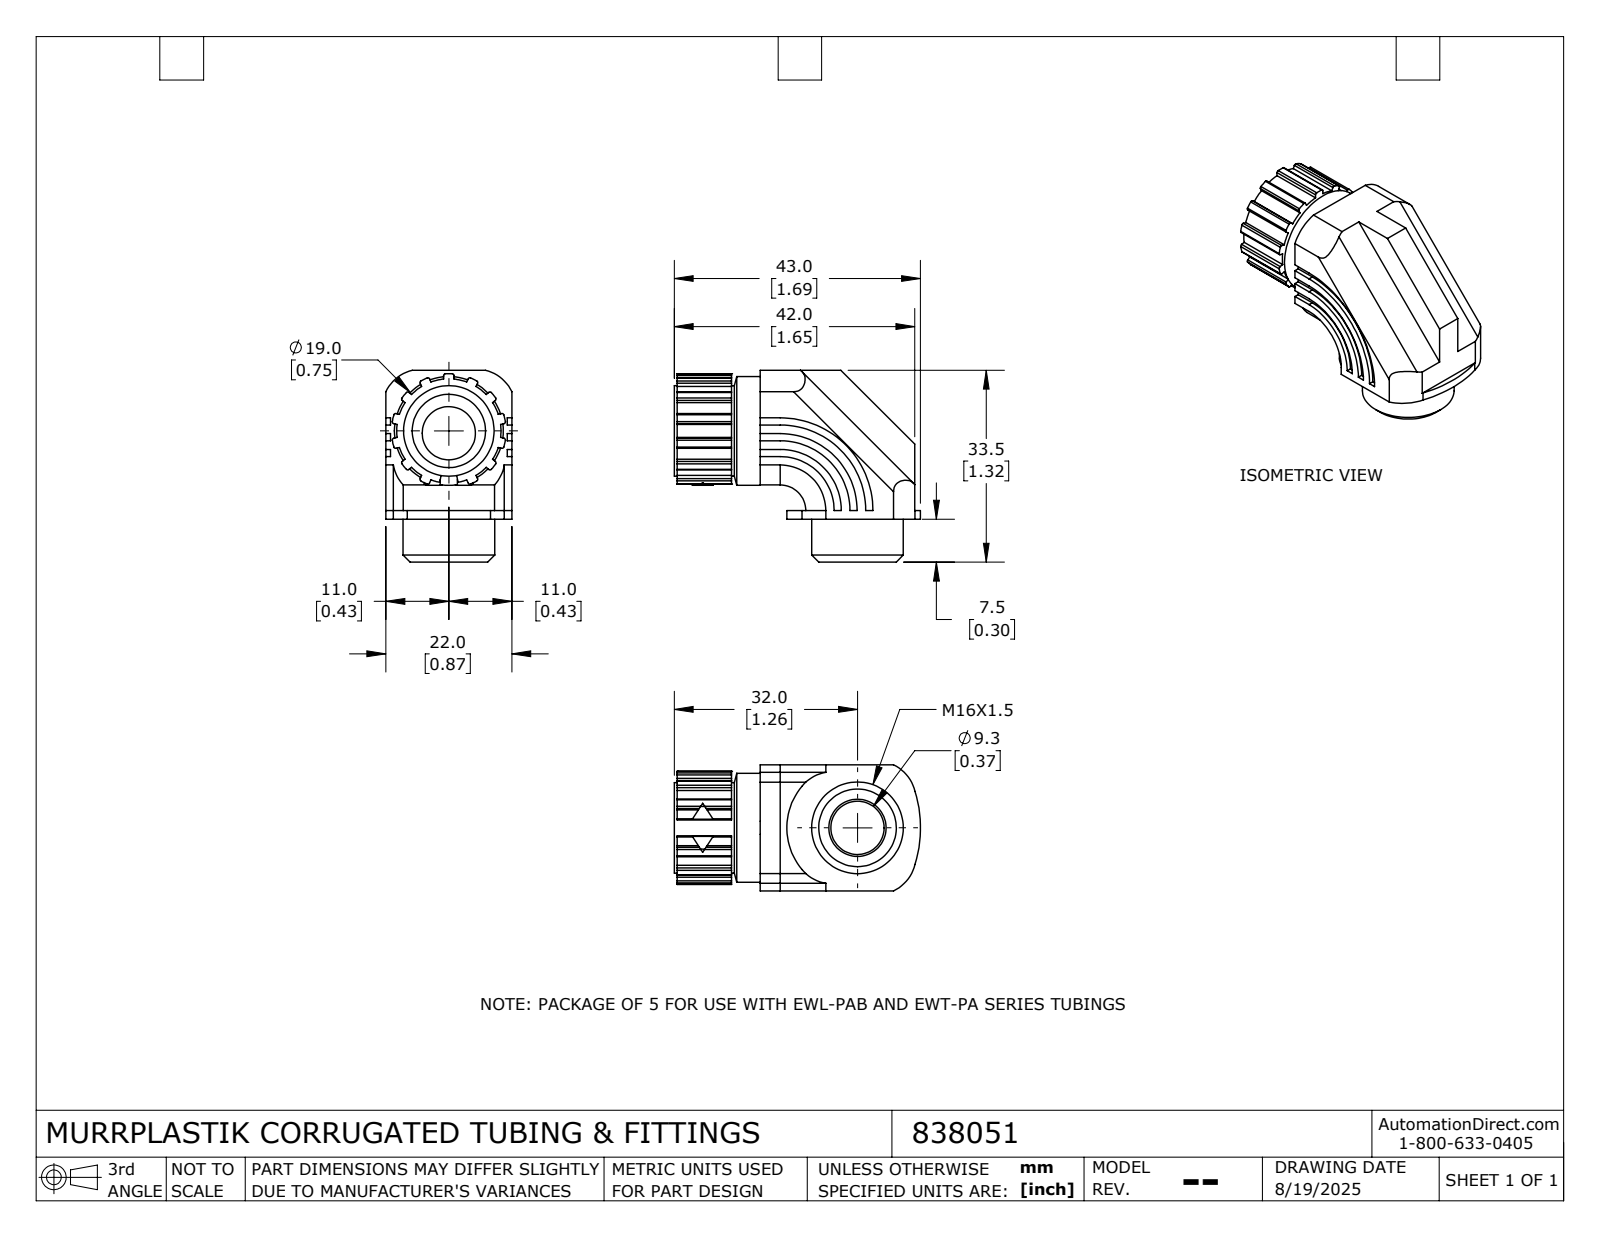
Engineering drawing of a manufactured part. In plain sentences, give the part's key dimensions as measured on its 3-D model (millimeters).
The part is named "838051_Default". Its 3-D file was written by "SolidWorks 2024 (CONFIG_CONTROL_DESIGN)". It is 1 solid with 185 faces: 87 planar, 93 cylindrical and 5 other. Overall it measures 43 by 33.5 by 22 millimeters. Its volume is 11 325 cubic millimeters and its surface area 6 342 square millimeters. Round holes: 2 of diameter 9.3, 1 of diameter 10, 1 of diameter 12.8. Round bosses or shafts: 1 of diameter 19, 1 of diameter 16, 1 of diameter 15.8. Partial cylindrical surfaces (rounded edges, fillets, slot ends): 26 of radius 0.3, 8 of radius 7, 2 of radius 3.5, 1 of radius 4.47, 1 of radius 7.96, 1 of radius 9.1, 1 of radius 9.42, 1 of radius 10. The main face-to-face distances are 8.75, 13.25, 22, 0.8, 21.2, 7.95, 12.45, 5, 26, 4.5. The hole center spacings are 0.4.
